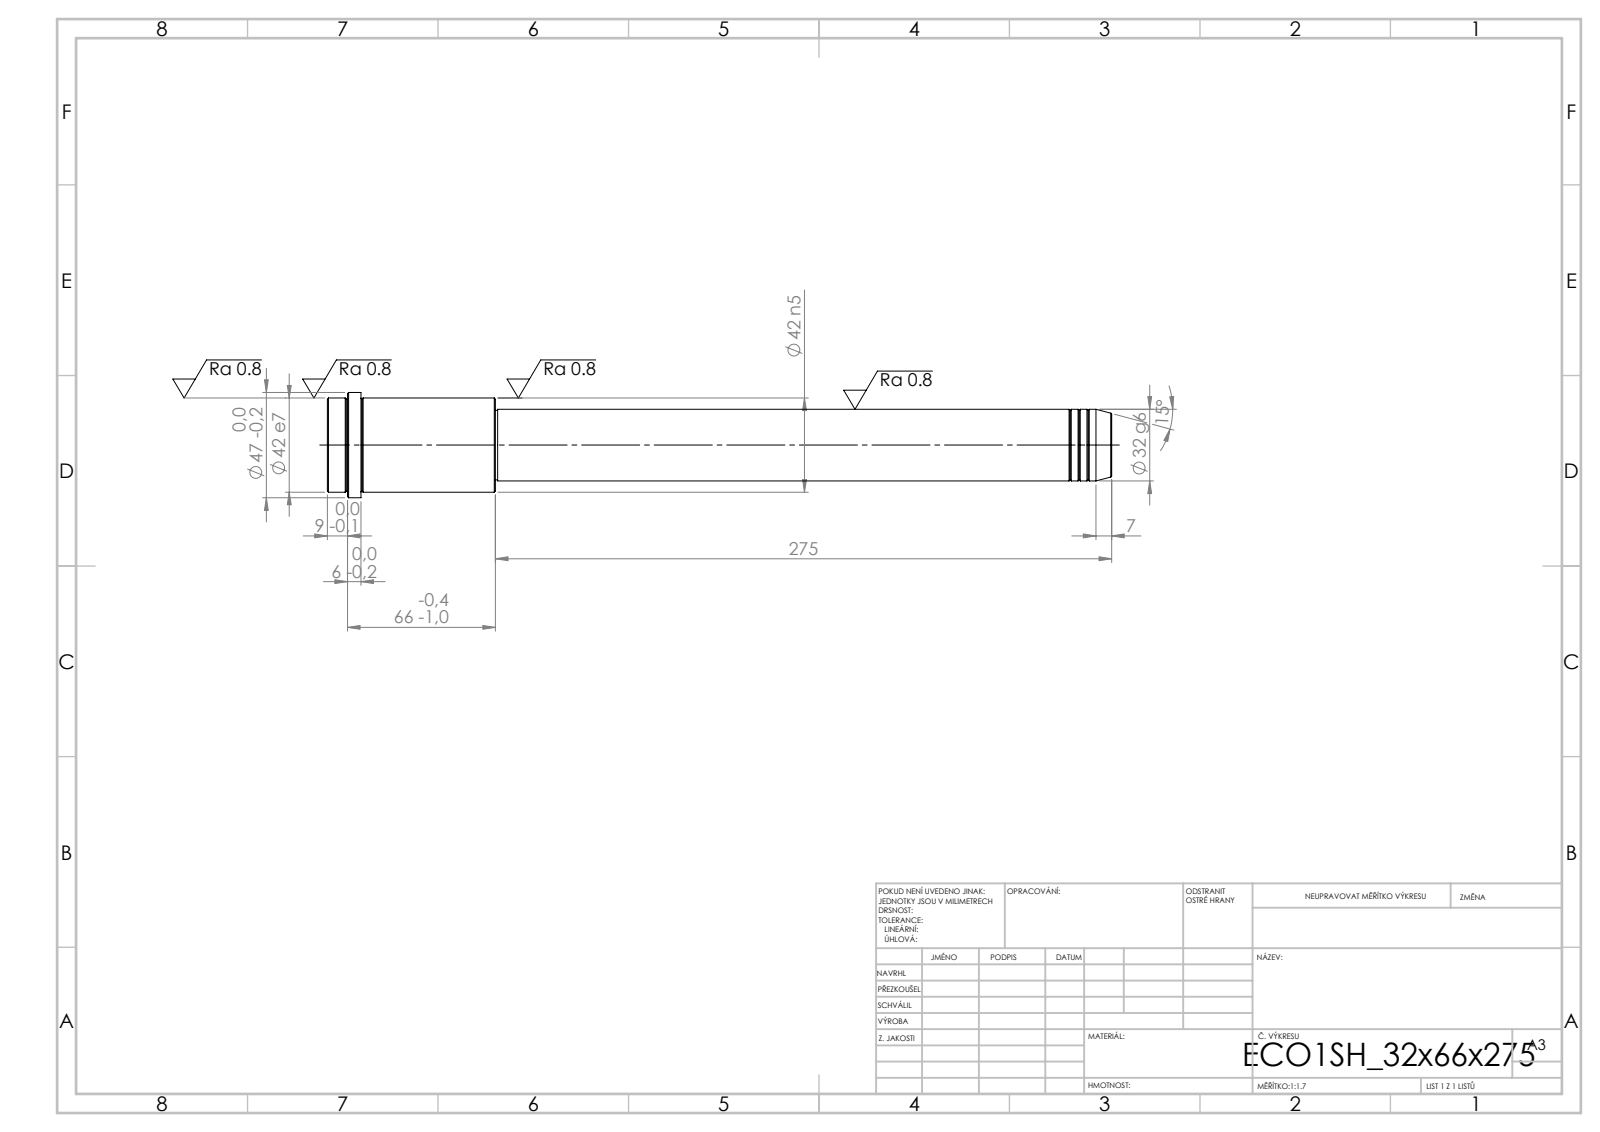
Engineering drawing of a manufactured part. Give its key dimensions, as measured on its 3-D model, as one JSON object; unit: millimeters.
{"step_written_by": "SolidWorks 2019 (CONFIG_CONTROL_DESIGN)", "units": "millimeters", "bodies": {"solids": 1, "faces": 52, "planar": 6, "cylindrical": 16, "other": 30}, "overall_size": [350, 47, 47], "volume_mm3": 326217, "surface_area_mm2": 41182, "round_bosses_or_shafts": [[47, 1], [42, 1], [32, 1], [31, 1]], "face_to_face_distances": [350, 275, 75, 335, 60, 15, 341, 66, 6, 9]}
